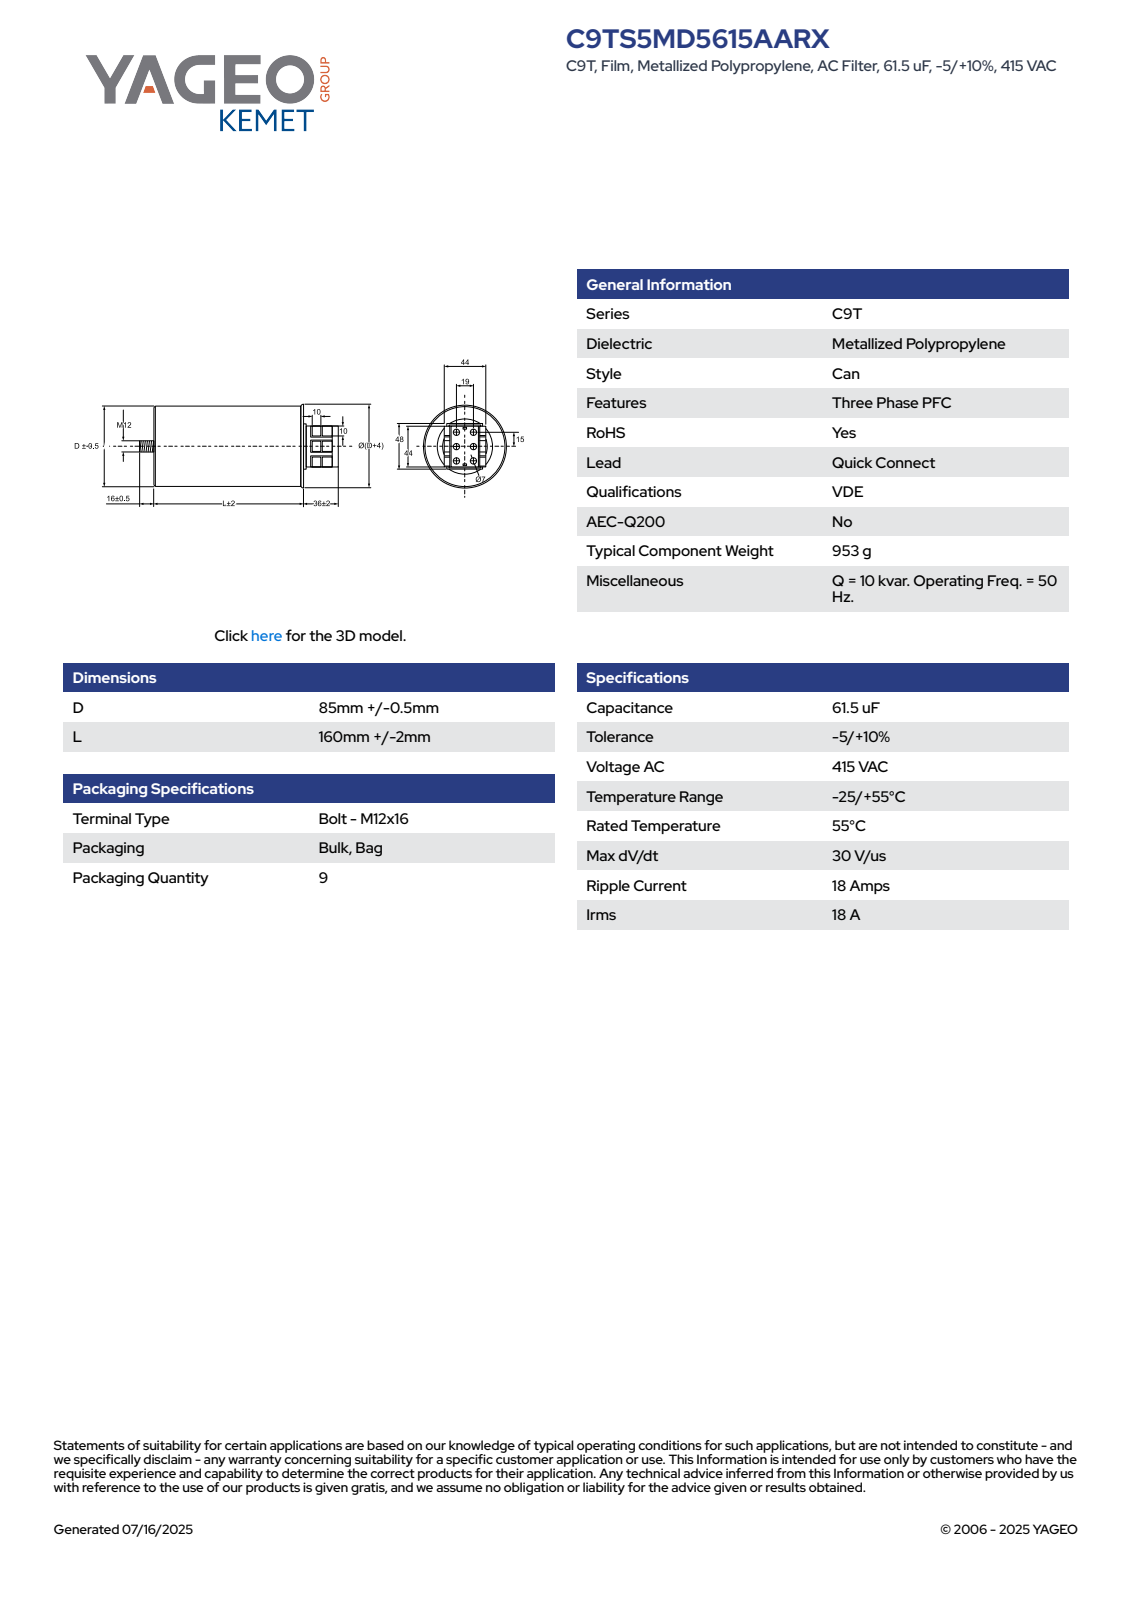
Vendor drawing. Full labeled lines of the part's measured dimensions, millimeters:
Part name (STEP PRODUCT): CFP_C9T_85X160_D85.5L162
STEP written by: SolidWorks 2014 (AUTOMOTIVE_DESIGN)
Units: millimetres
Bodies: 1 solid, 132 faces (78 planar, 19 cylindrical, 35 other)
Overall size (bounding box): 216.5 × 89.5 × 89.5
Volume: 966 918 mm³ · Surface area: 77 333 mm²
Round holes (diameter × count): ⌀7 ×6
Round bosses / shafts (diameter × count): ⌀85.5 ×1, ⌀12 ×1
Partial cylindrical surfaces — rounded edges, fillets, slot ends (radius × count): R42.76 ×1
Main face-to-face distances: 10, 162, 11.15, 15.85, 1.15, 4, 44, 166, 38, 17
Hole centre spacings: 15, 24.21, 19, 30, 35.51
